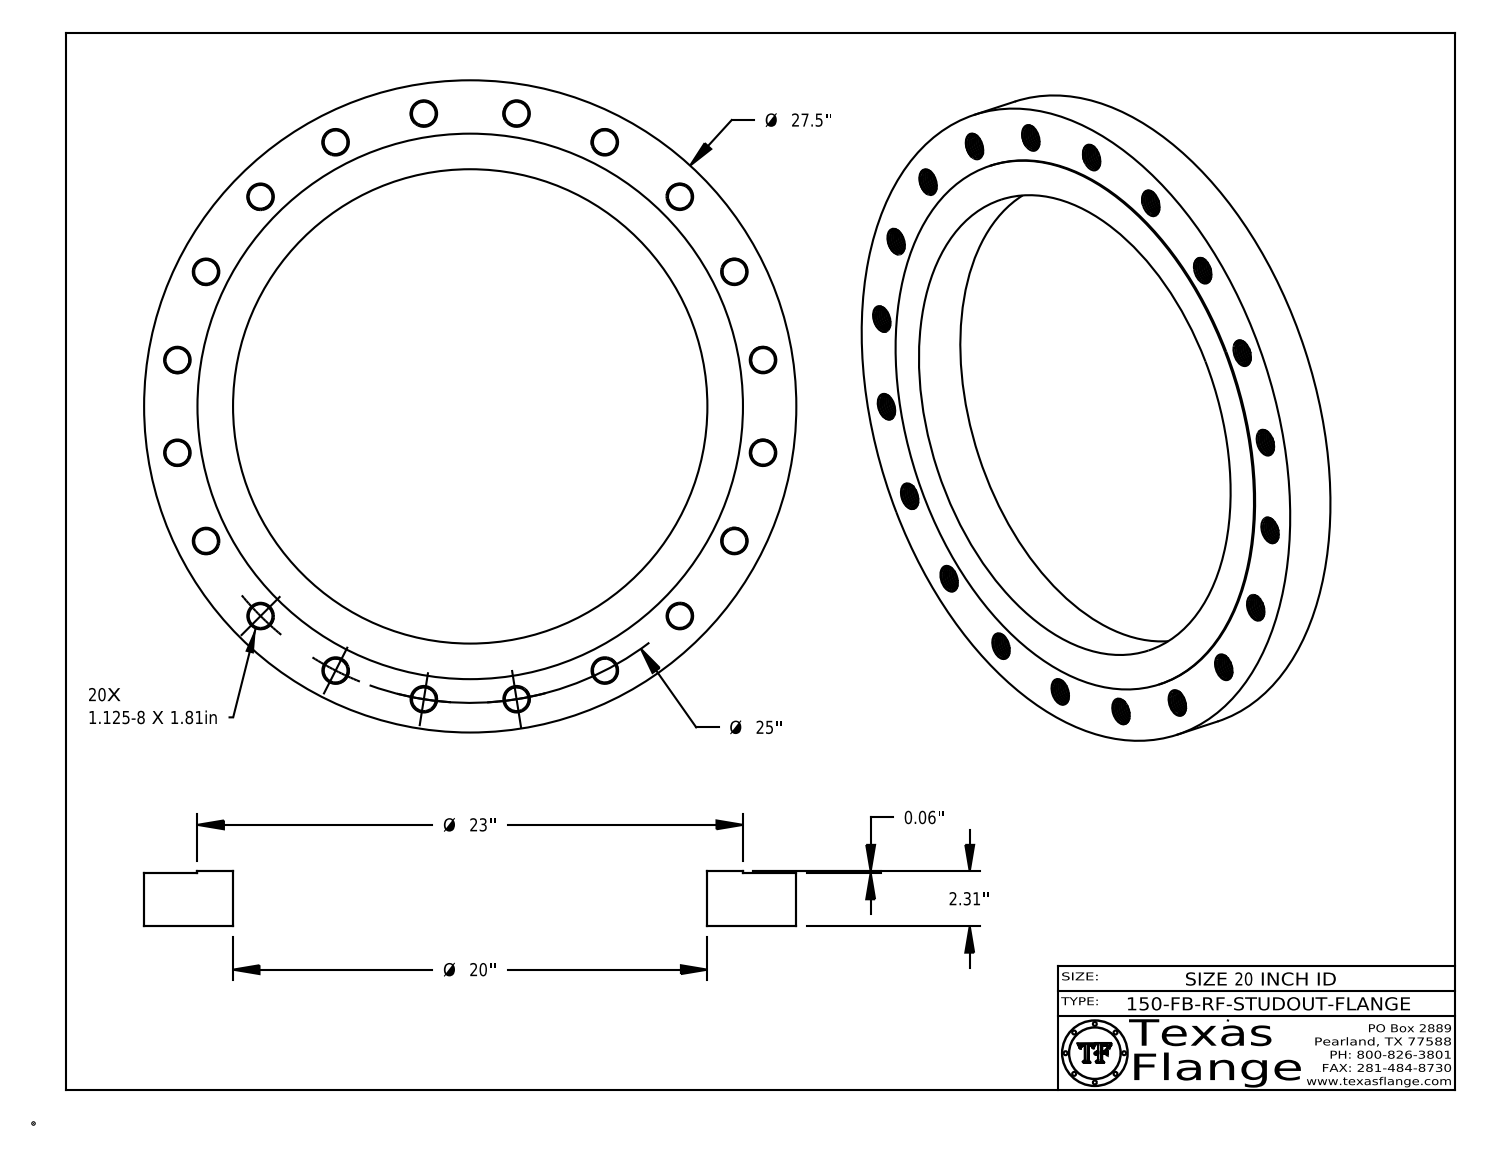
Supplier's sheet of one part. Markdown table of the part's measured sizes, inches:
| quantity | value |
| --- | --- |
| part name | 20-150-FB-RF-STUDOUT-FLANGE |
| STEP written by | CATIA V5 STEP AP214 (AUTOMOTIVE_DESIGN) |
| units | inches |
| bodies | 1 solid, 1754 faces (368 planar, 466 cylindrical, 920 other) |
| overall size | 27.5 × 27.5 × 2.313 |
| volume | 603.5 in³ |
| surface area | 1 054 in² |
| round holes (diameter × count) | 1 × 21, 20 × 1 |
| round bosses / shafts (diameter × count) | 0.061 × 8, 27.5 × 1, 23 × 1, 0.788 × 1 |
| main face-to-face distances | 2.25, 0.063, 2.313, 2.298, 2.235, 0.015, 0.298, 0.293, 0.054, 0.248 |
| hole center spacings | 14.694, 24.692, 12.5, 7.726, 17.678, 22.275, 3.911, 11.35 |
